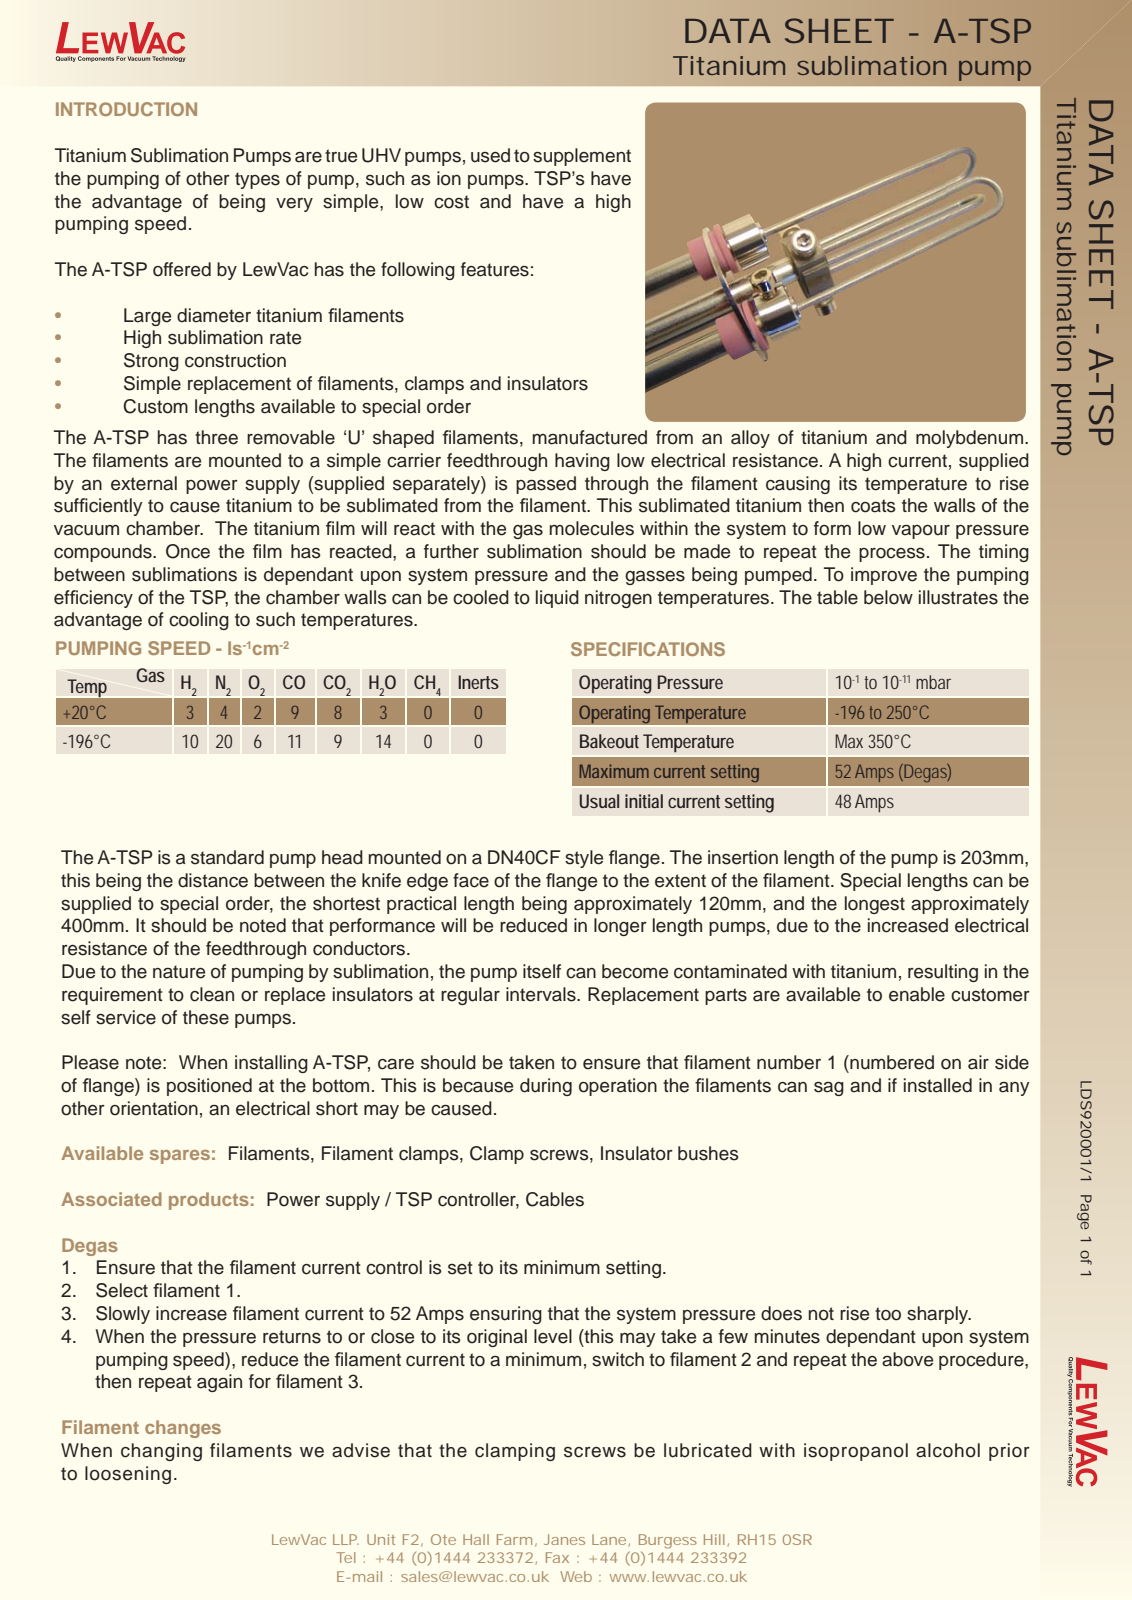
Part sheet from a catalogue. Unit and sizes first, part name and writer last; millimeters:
Units: millimetres
Overall size (bounding box): 253.5 × 69.85 × 69.85
Round holes (diameter × count): ⌀6.8 ×9, ⌀5.3 ×4, ⌀1.7 ×3, ⌀2 ×3, ⌀2.3 ×3, ⌀2.5 ×3, ⌀3.2 ×3, ⌀6.6 ×3, ⌀10.2 ×3, ⌀11.5 ×3, ⌀12.25 ×3, ⌀3.61 ×1
Round bosses / shafts (diameter × count): ⌀3 ×7, ⌀5.5 ×6, ⌀2 ×6, ⌀10 ×4, ⌀6 ×4, ⌀5 ×4, ⌀13 ×3, ⌀12.2 ×3
Partial cylindrical surfaces — rounded edges, fillets, slot ends (radius × count): R0.5 ×4, R1.18 ×3, R3 ×1, R3.12 ×1, R8.5 ×1
Main face-to-face distances: 12.9, 1.2, 11.7, 13, 11.8, 13.92, 12.72, 1.02, 0.92, 134.98
Hole centre spacings: 29.35, 39.27, 43.4, 50.84, 20.57, 26.08, 31.35, 11
Volume: 72 729 mm³ · Surface area: 45 941 mm²
Bodies: 11 solids, 633 faces (216 planar, 249 cylindrical, 168 other)
Part name (STEP PRODUCT): PRT0001
STEP written by: CREO PARAMETRIC BY PTC INC, 2015080 (AUTOMOTIVE_DESIGN)
